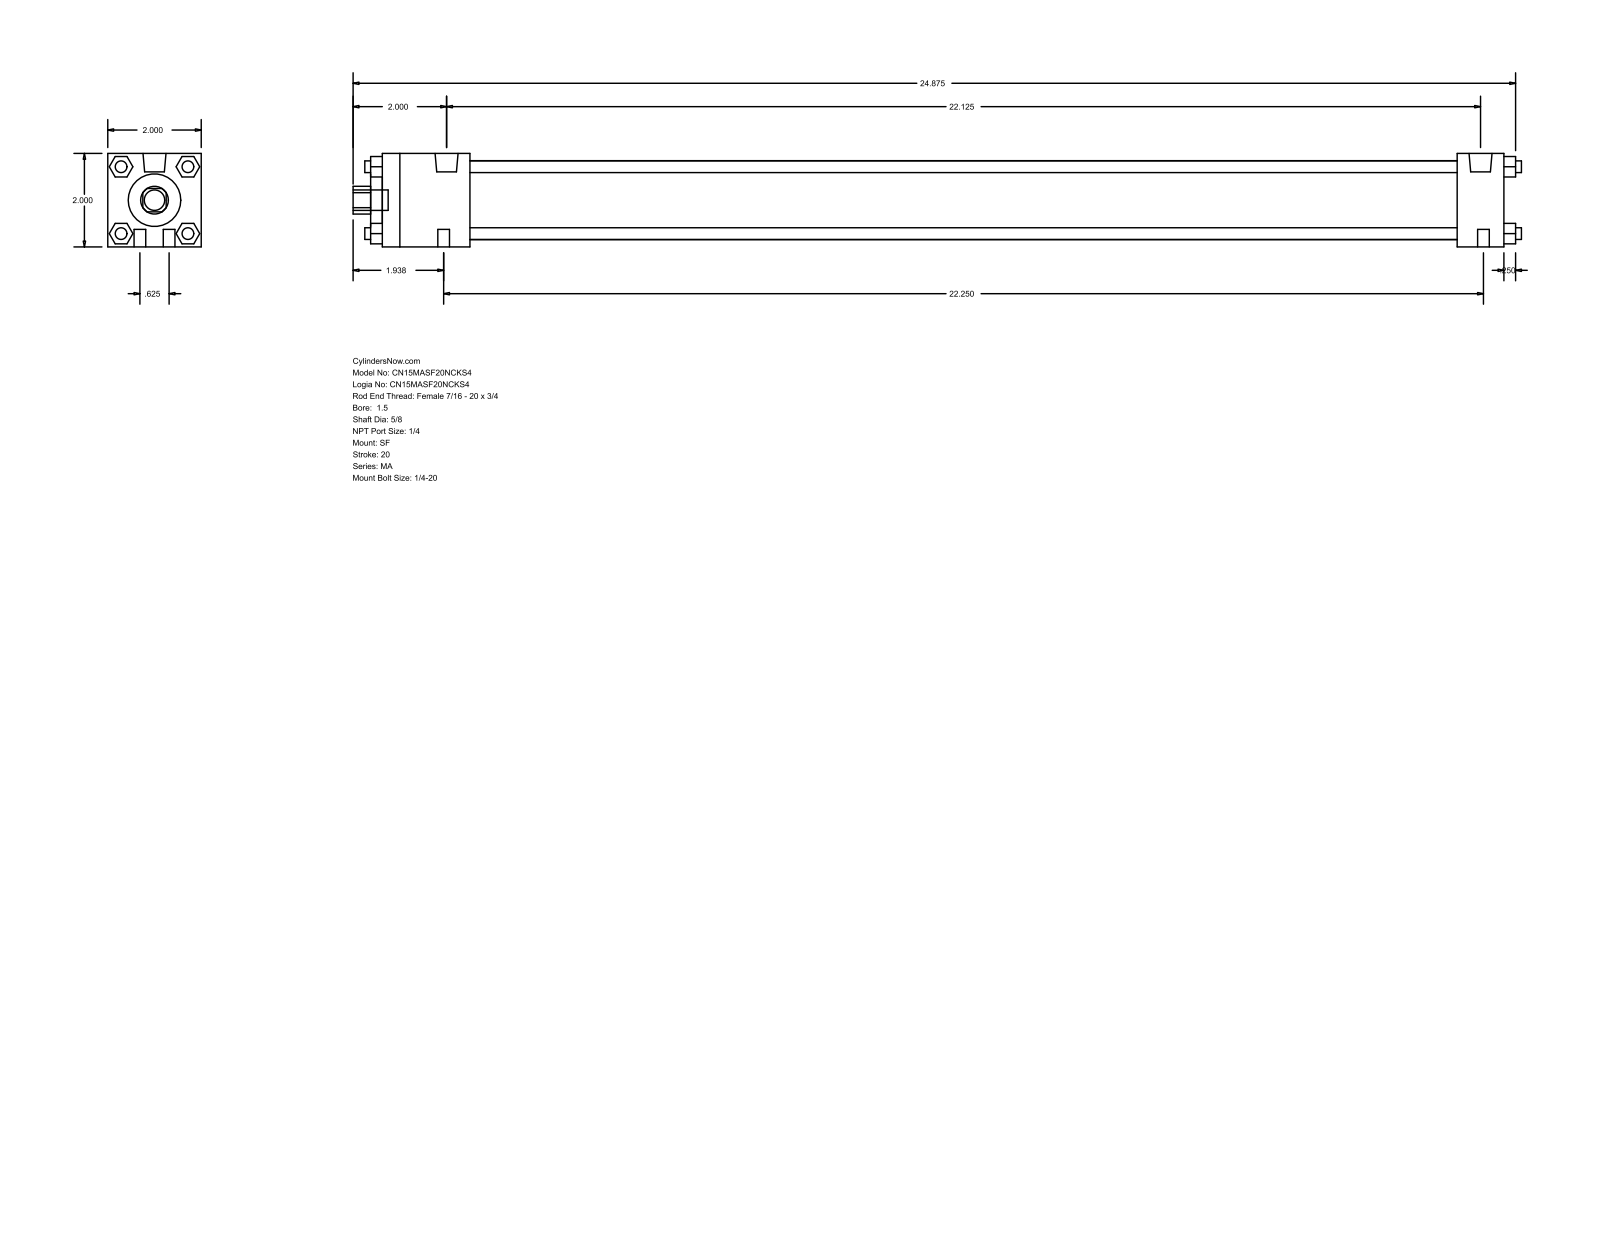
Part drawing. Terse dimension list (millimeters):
name: MA_SF__0150_0.625
written by: GSSL Pune (CONFIG_CONTROL_DESIGN)
unit: mm
bodies: 0 solids, 124 faces (94 planar, 30 cylindrical, 0 other)
size: 635 × 50.8 × 50.8
holes: 1× ⌀15.88, 1× ⌀28.57, 1× ⌀42.93
bosses: 8× ⌀6.35, 2× ⌀12.49, 2× ⌀7.94, 1× ⌀11.11
rounds: 1× R7.54
face distances: 50.8, 609.6, 6.35, 615.95, 47.62, 584.2, 536.58, 561.98, 25.4, 53.97
